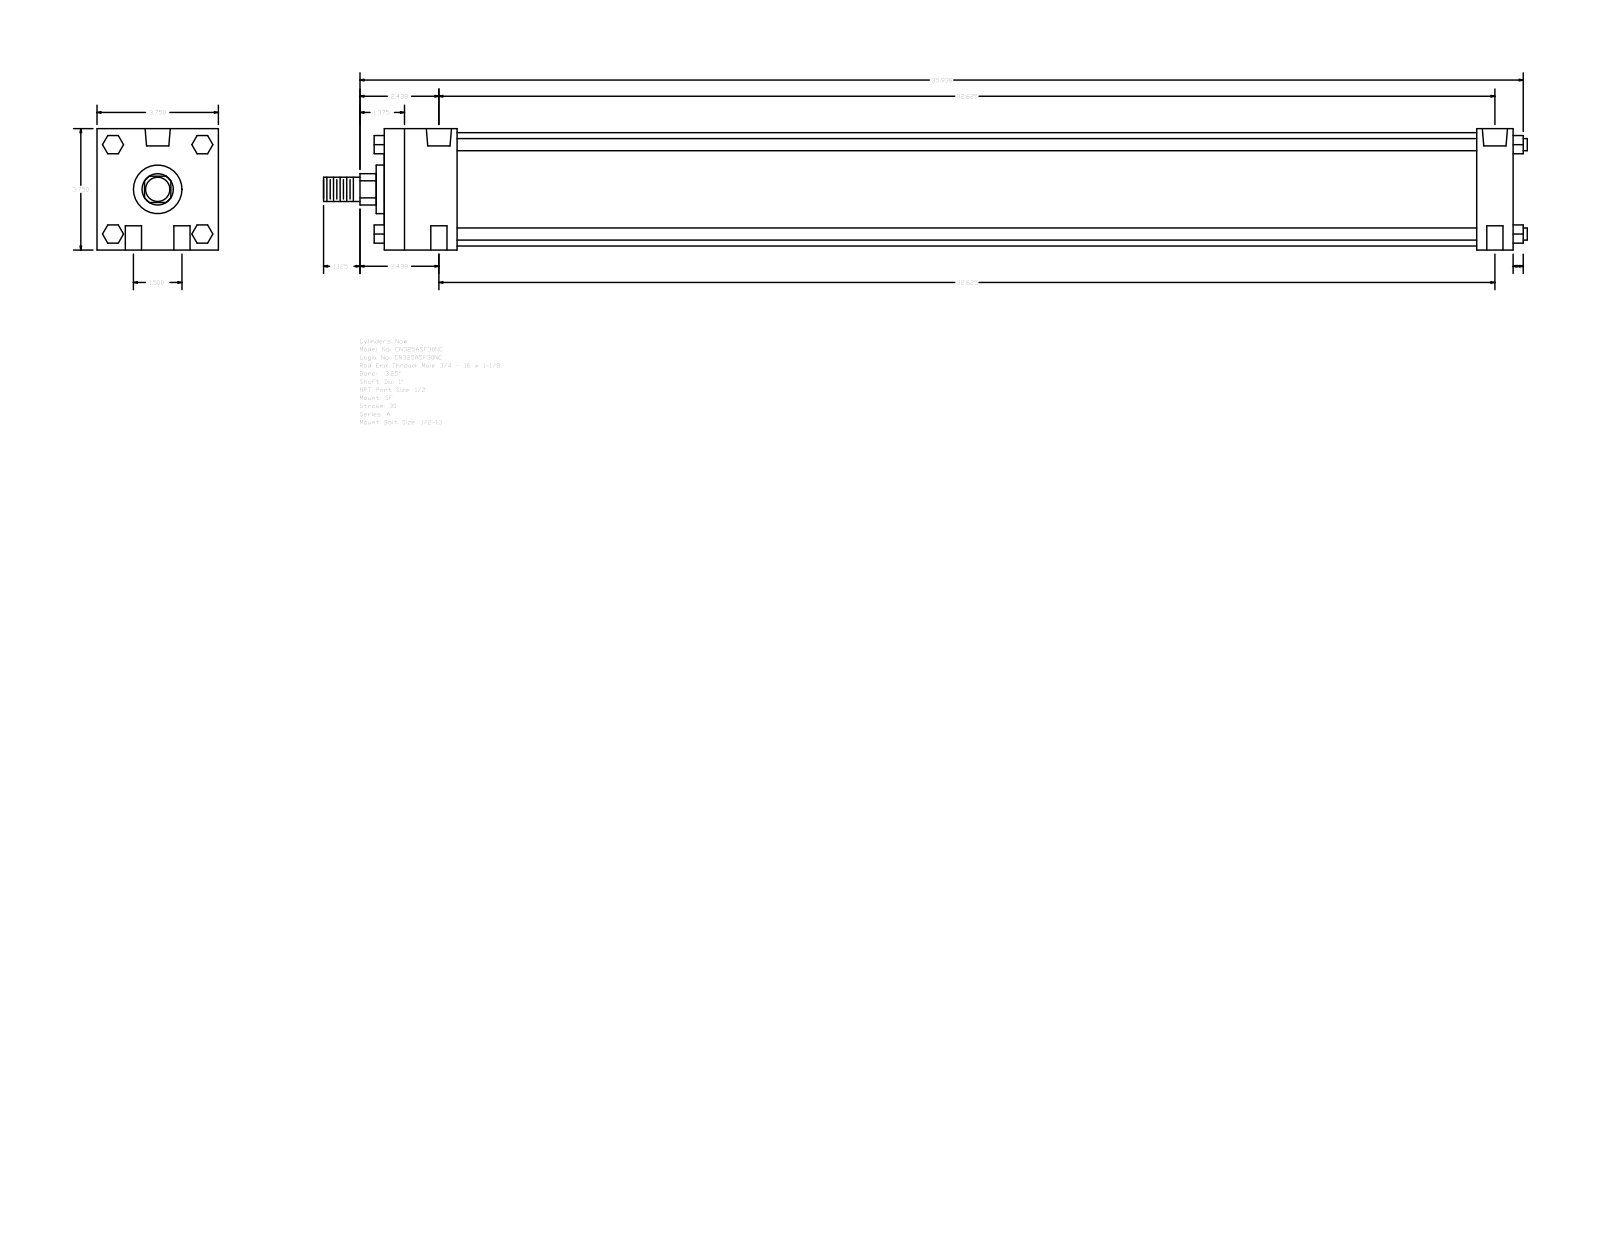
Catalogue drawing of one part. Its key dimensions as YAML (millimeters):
part_name: "A_SF__0325_1"
step_written_by: "GSSL Pune (CONFIG_CONTROL_DESIGN)"
units: millimeters
bodies: {solids: 0, faces: 124, planar: 94, cylindrical: 30, other: 0}
overall_size: [944.56, 95.25, 95.25]
round_holes:
  - {diameter: 12.7, count: 4}
  - {diameter: 8.73, count: 2}
  - {diameter: 19.77, count: 2}
round_bosses_or_shafts:
  - {diameter: 9.53, count: 4}
  - {diameter: 88.9, count: 1}
  - {diameter: 38.1, count: 1}
  - {diameter: 25.4, count: 1}
  - {diameter: 19.05, count: 1}
partial_cylinders:
  - {radius: 12.29, count: 1}
face_to_face_distances: [95.24, 885.83, 857.25, 28.58, 57.15, 800.1, 828.68, 14.28, 35.05, 60.71]
hole_center_spacings: [19.05, 828.9, 828.68, 38.1, 829.56, 822.32]
